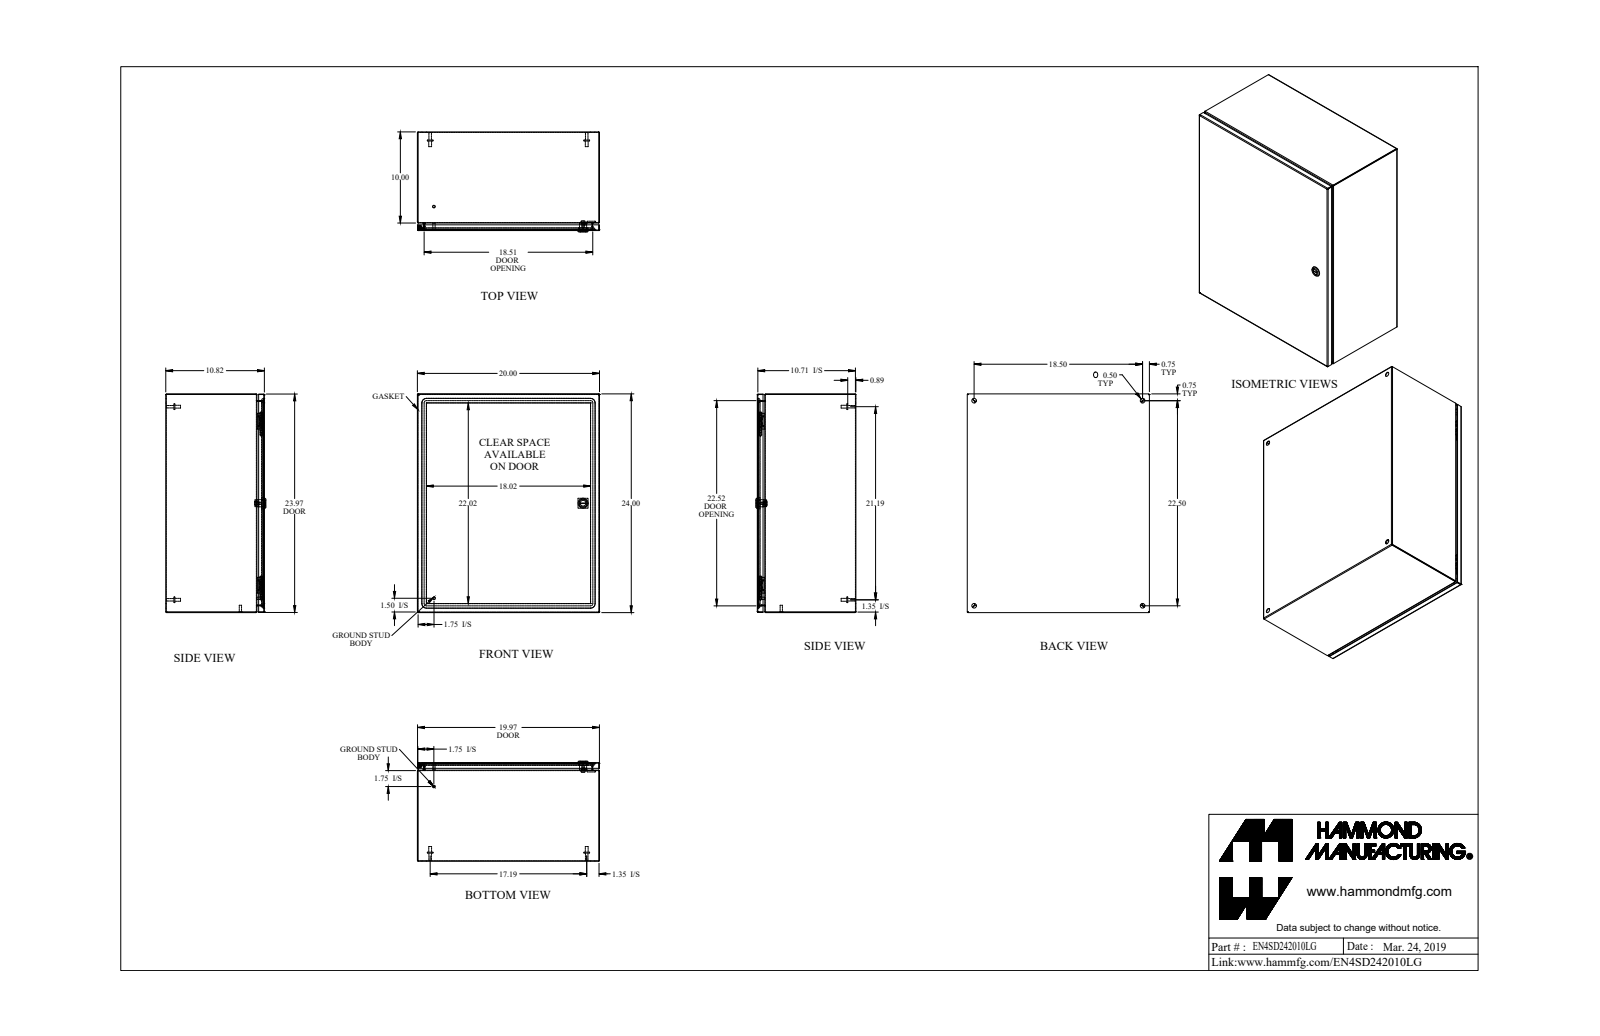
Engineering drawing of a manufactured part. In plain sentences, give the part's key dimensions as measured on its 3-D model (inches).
The part is named "EN4SD242010LG_Default". Its 3-D file was written by "SolidWorks 2019 (CONFIG_CONTROL_DESIGN)". It is 21 solids with 634 faces: 285 planar, 213 cylindrical and 136 other. Overall it measures 24 by 20 by 10.982 inches. Its volume is 123.2 cubic inches and its surface area 4 216 square inches. Round holes: 4 of diameter 0.5, 1 of diameter 0.172, 1 of diameter 0.232, 1 of diameter 0.24, 1 of diameter 0.242, 1 of diameter 0.625, 1 of diameter 0.785. Round bosses or shafts: 4 of diameter 0.625, 4 of diameter 0.313, 4 of diameter 0.27, 2 of diameter 0.281, 2 of diameter 0.25, 1 of diameter 1.1, 1 of diameter 0.525, 1 of diameter 0.455. Partial cylindrical surfaces (rounded edges, fillets, slot ends): 21 of radius 0.029, 21 of radius 0.086, 16 of radius 0.25, 8 of radius 19, 4 of radius 0.006, 4 of radius 0.062, 4 of radius 0.499, 2 of radius 0.125. The main face-to-face distances are 0.057, 10.765, 10.708, 10.822, 19.943, 23.943, 19.886, 20, 23.886, 24. The hole center spacings are 18.5, 22.5, 29.129, 11.299, 11.3, 20.754, 20.755.
